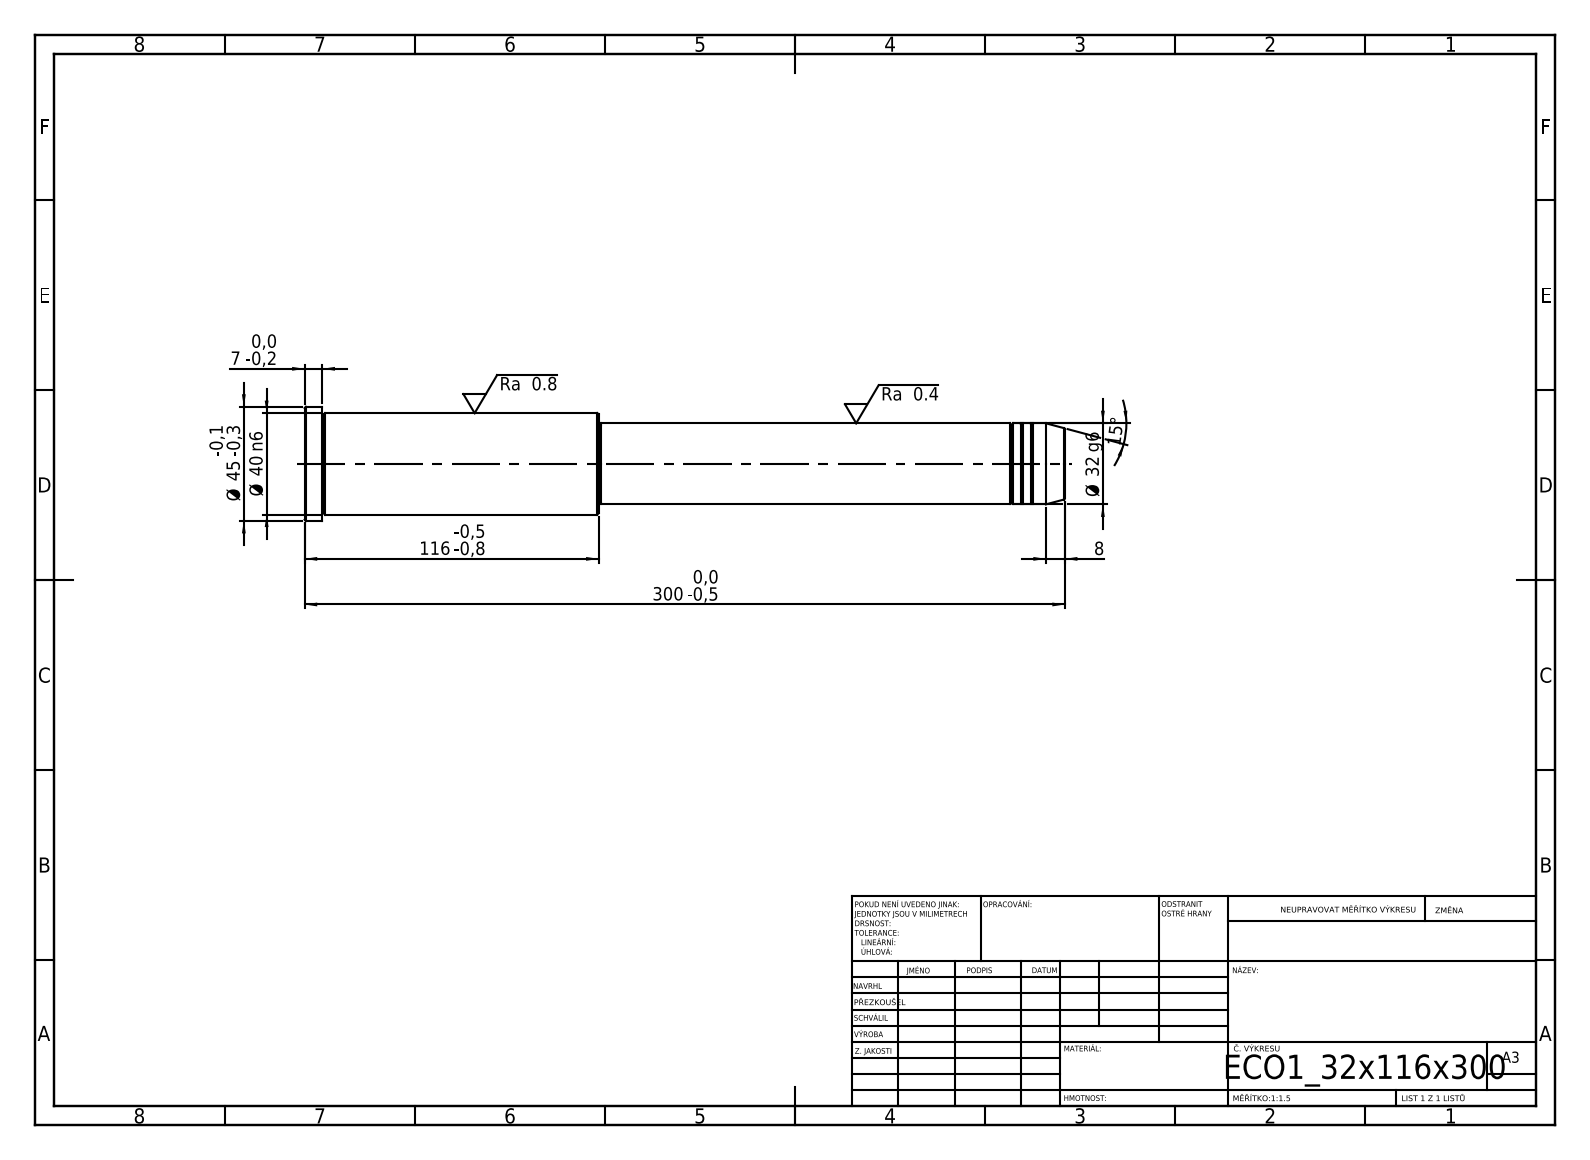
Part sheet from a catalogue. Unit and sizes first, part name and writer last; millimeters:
Units: millimetres
Overall size (bounding box): 300 × 45 × 45
Round bosses / shafts (diameter × count): ⌀45 ×1, ⌀40 ×1, ⌀32 ×1, ⌀31 ×1
Main face-to-face distances: 300, 184, 116, 293, 109, 7, 183, 1, 110, 117
Volume: 295 111 mm³ · Surface area: 36 392 mm²
Bodies: 1 solid, 43 faces (5 planar, 14 cylindrical, 24 other)
STEP written by: SolidWorks 2019 (CONFIG_CONTROL_DESIGN)
